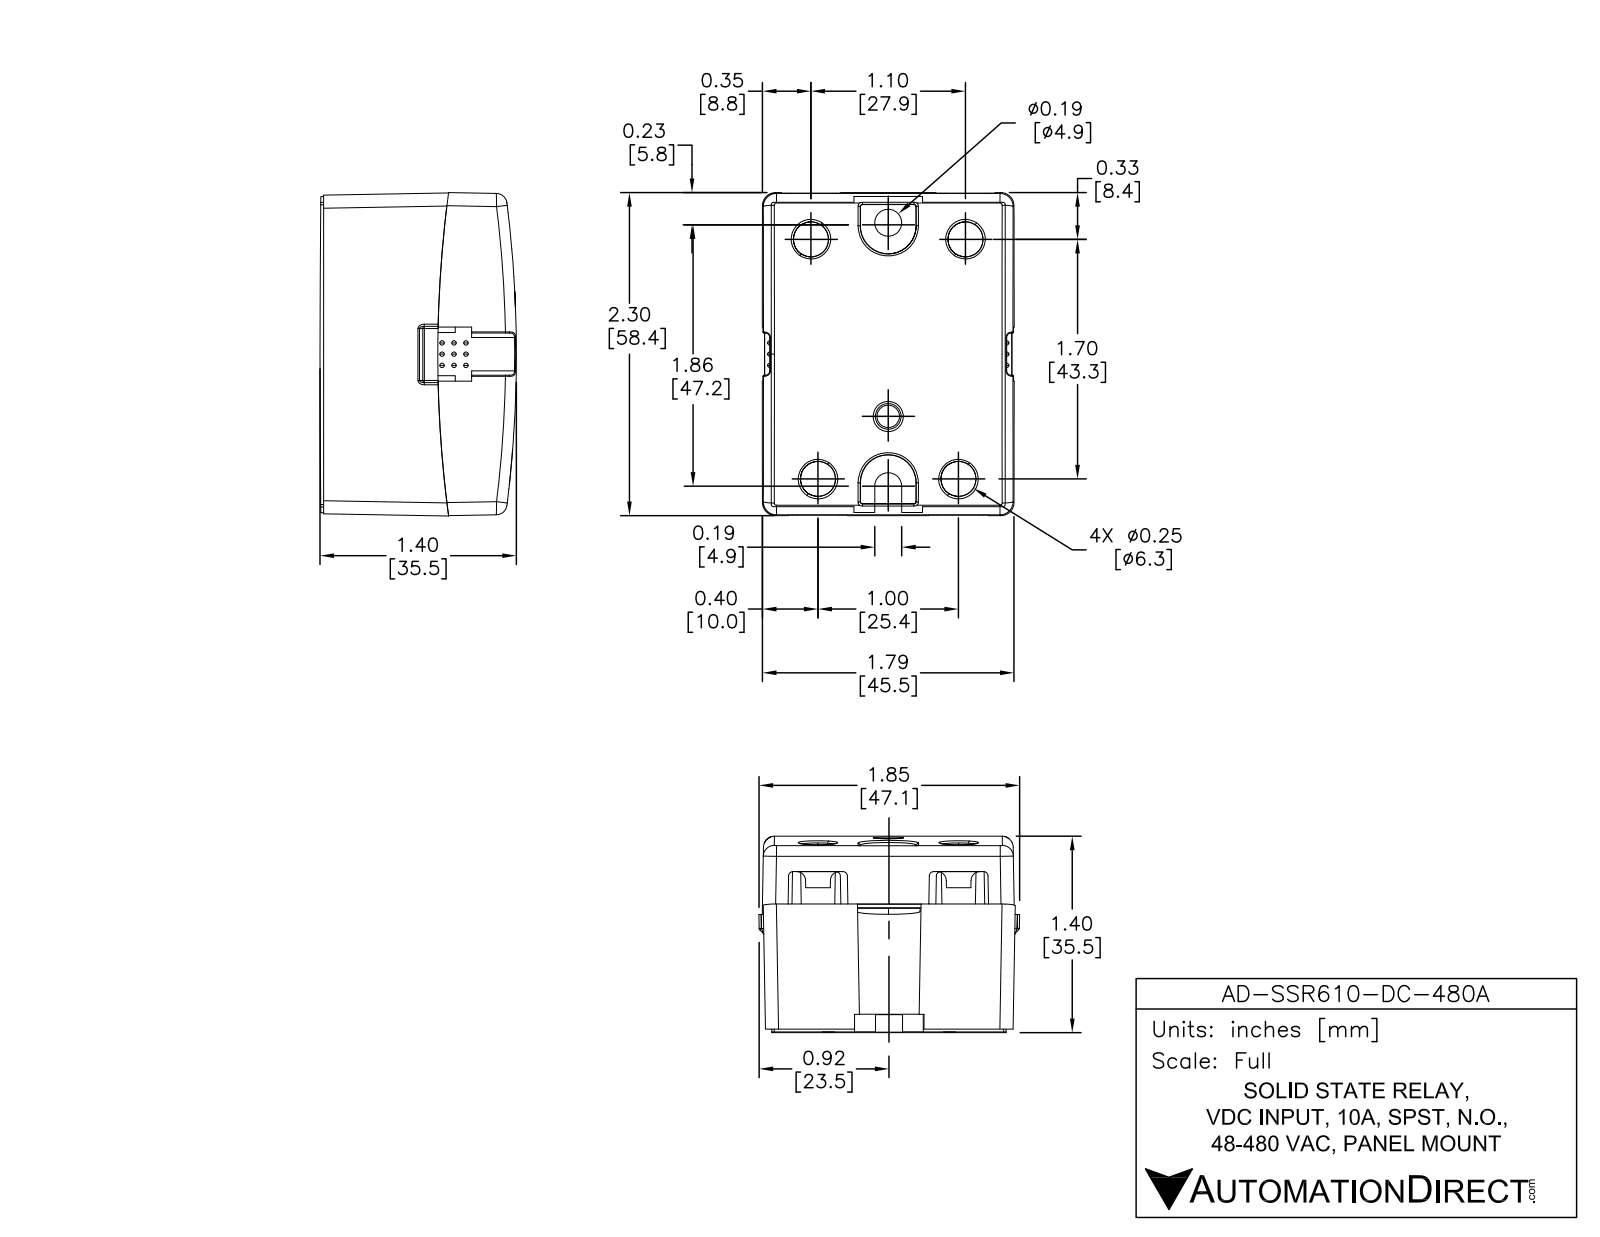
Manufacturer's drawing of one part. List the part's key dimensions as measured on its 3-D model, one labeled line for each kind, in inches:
Part name (STEP PRODUCT): AD-SSR610-DC-480A
STEP written by: SolidWorks 2013 (AUTOMOTIVE_DESIGN)
Units: inches
Bodies: 3 solids, 251 faces (145 planar, 95 cylindrical, 11 other)
Overall size (bounding box): 2.3 × 1.79 × 1.4
Volume: 5.14 in³ · Surface area: 26.41 in²
Round holes (diameter × count): ⌀0.25 ×4, ⌀0.19 ×1
Round bosses / shafts (diameter × count): ⌀0.4 ×2, ⌀0.35 ×2, ⌀0.3 ×2, ⌀0.25 ×2, ⌀0.2 ×2, ⌀0.2 ×2
Partial cylindrical surfaces — rounded edges, fillets, slot ends (radius × count): R0.03 ×6, R0.01 ×4, R0.04 ×4, R0.5 ×4, R0.194 ×2, R0.095 ×1, R0.5 ×1, R0.5 ×1
Main face-to-face distances: 1.79, 2.3, 1.166, 0.25, 0.916, 0.671, 1.059, 0.5, 1.8, 0.08
Hole centre spacings: 0.556, 0.565, 1, 1.1, 1.7, 1.701, 1.876, 1.879
